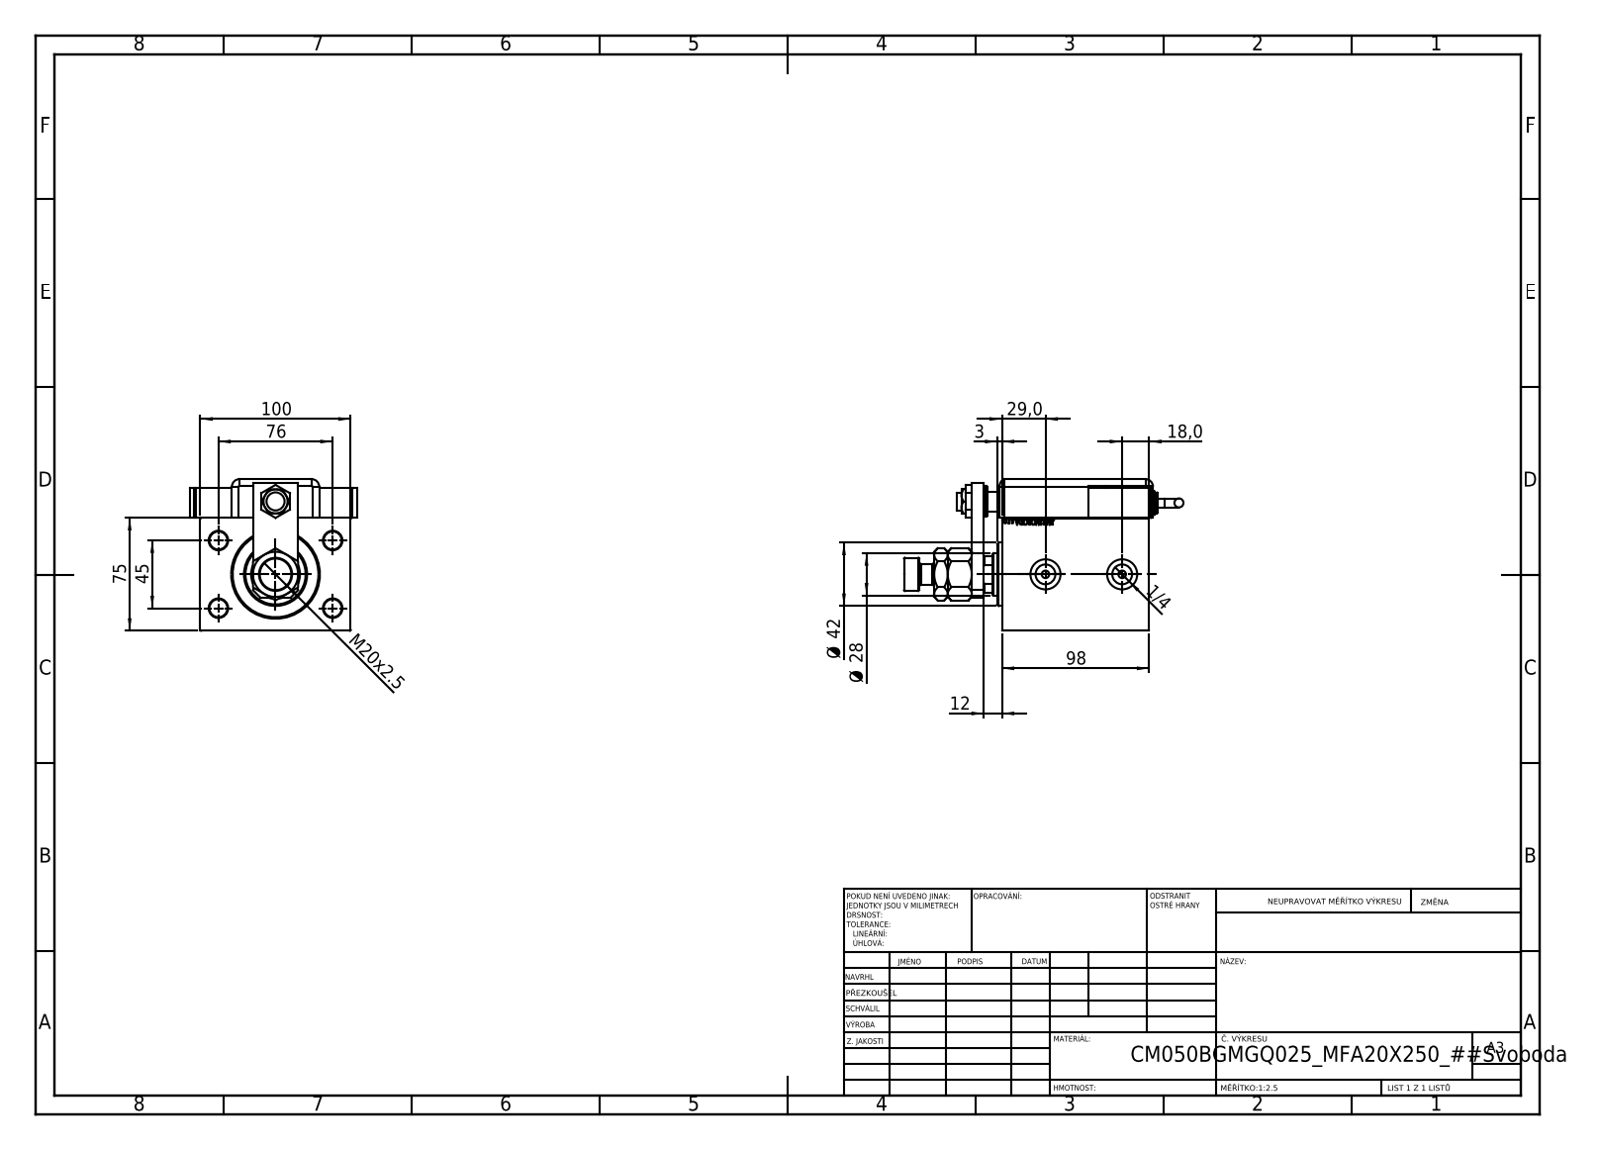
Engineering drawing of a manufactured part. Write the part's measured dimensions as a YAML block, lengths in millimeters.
part_name: "NUT_D19; V450CM_B_VCP; KRYT; NUT_D13 (+7 more)"
step_written_by: "SolidWorks 2019 (CONFIG_CONTROL_DESIGN)"
units: millimeters
bodies: {solids: 14, faces: 1320, planar: 624, cylindrical: 115, other: 581}
overall_size: [185.76, 111, 100.8]
volume: 845639
surface_area: 154516
round_holes:
  - {diameter: 12, count: 5}
  - {diameter: 20, count: 3}
  - {diameter: 4, count: 2}
  - {diameter: 5, count: 2}
  - {diameter: 8, count: 2}
  - {diameter: 13.16, count: 2}
  - {diameter: 13, count: 1}
  - {diameter: 14, count: 1}
  - {diameter: 18.5, count: 1}
  - {diameter: 28, count: 1}
  - {diameter: 31.5, count: 1}
  - {diameter: 32.5, count: 1}
round_bosses_or_shafts:
  - {diameter: 20, count: 3}
  - {diameter: 14, count: 3}
  - {diameter: 16, count: 2}
  - {diameter: 6, count: 2}
  - {diameter: 42, count: 1}
  - {diameter: 22, count: 1}
partial_cylinders:
  - {radius: 5, count: 9}
  - {radius: 10, count: 1}
  - {radius: 13.5, count: 1}
face_to_face_distances: [75, 3, 98, 100, 14, 20, 84, 25.8, 100.8, 13.5]
hole_center_spacings: [44.16, 45, 46.04, 76, 80.53, 88.32, 20, 48.5]
